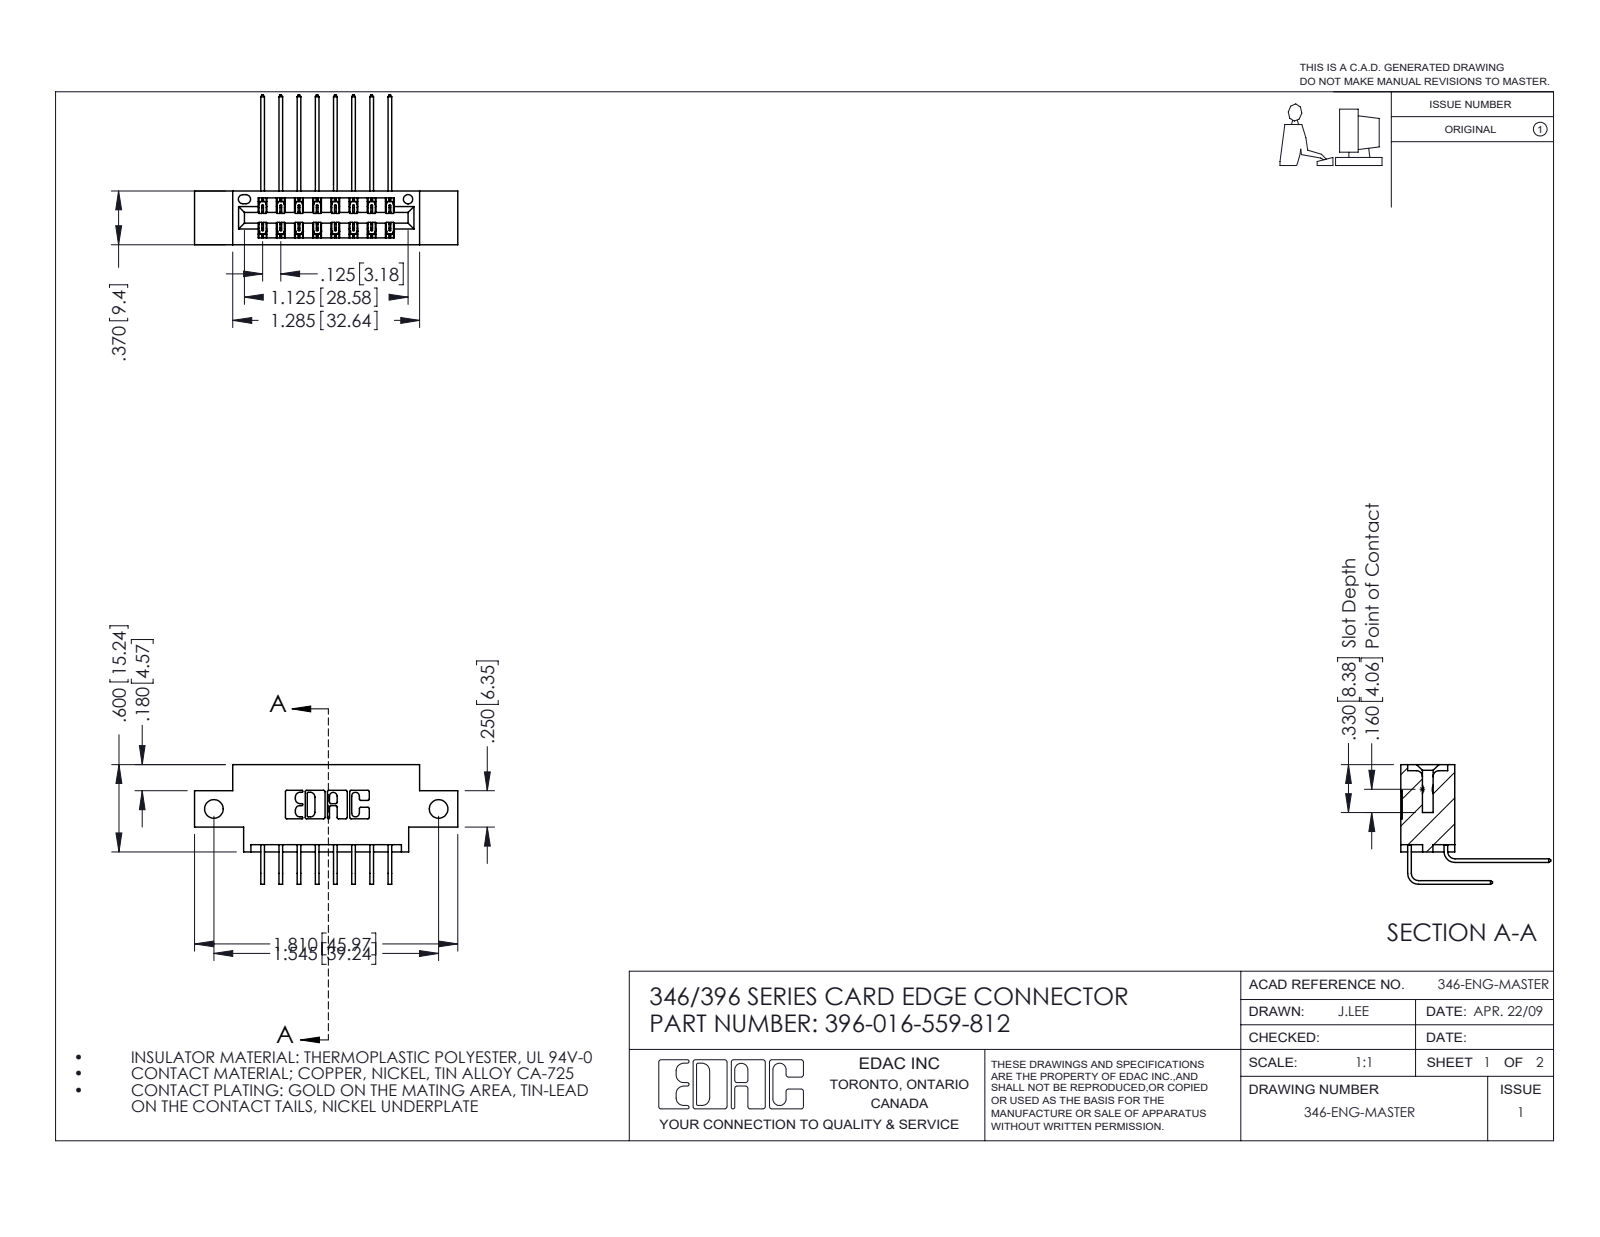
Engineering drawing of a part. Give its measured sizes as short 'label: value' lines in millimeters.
name: 345-292-001_558 559 Tail - 1; 346 Part_0.170 Offset - Side Mount; 345-292-001_559 Tail - 2; 396-016-559-812
written by: SolidWorks 2016 (CONFIG_CONTROL_DESIGN)
unit: mm
bodies: 17 solids, 990 faces (672 planar, 318 cylindrical, 0 other)
size: 46 × 26.2 × 20.9
volume: 4 060 mm³; area: 5 545 mm²
holes: 2× ⌀3.3, 1× ⌀1.6
rounds: 24× R0.2, 22× R0.3, 6× R0.2, 6× R0.8, 3× R0.7, 2× R0.4, 2× R0.6, 2× R0.6
face distances: 6.4, 1.2, 9.4, 8.2, 0.6, 1.8, 7.6, 3.8, 5.6, 2.5
hole spacings: 39.2
